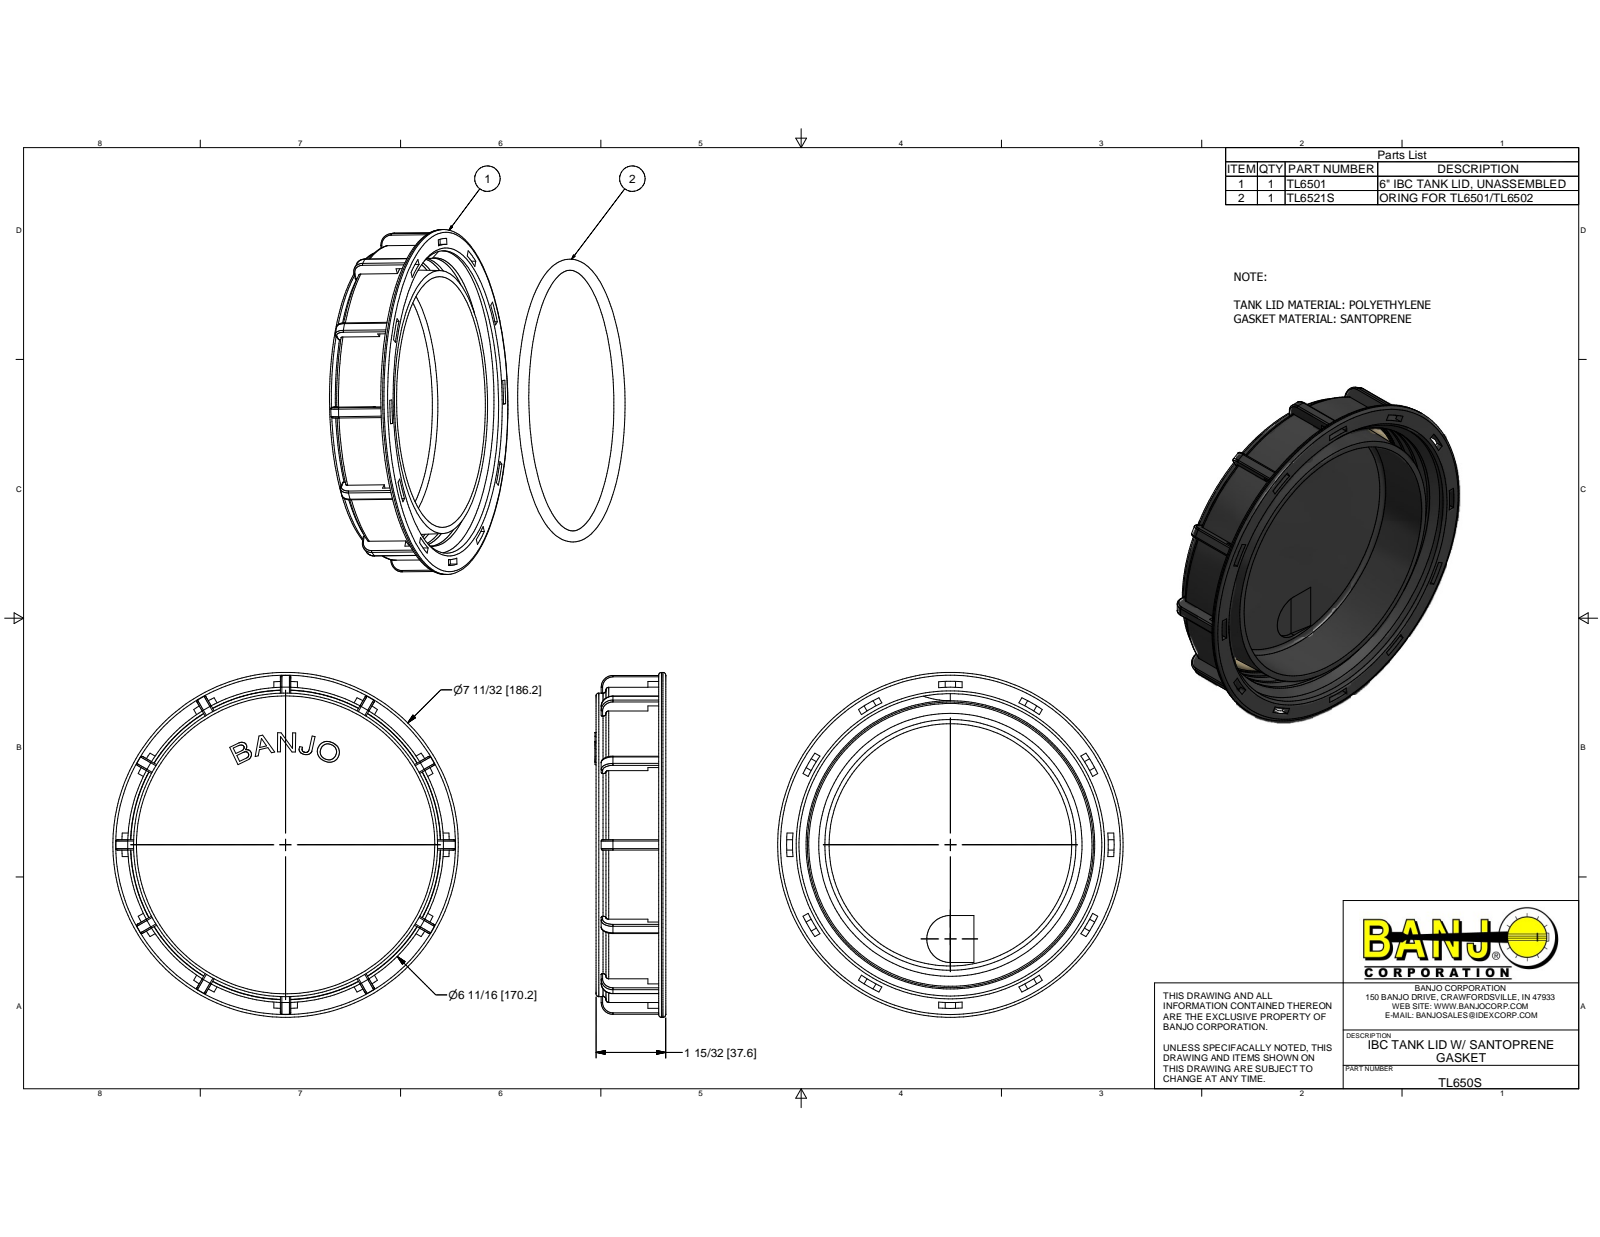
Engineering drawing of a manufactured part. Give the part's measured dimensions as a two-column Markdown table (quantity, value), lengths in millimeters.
| quantity | value |
| --- | --- |
| part name | TL650S; TL6501; TL6521S |
| STEP written by | Autodesk Inventor 2022 (AUTOMOTIVE_DESIGN) |
| units | millimeters |
| bodies | 2 solids, 329 faces (153 planar, 87 cylindrical, 89 other) |
| overall size | 186.2 × 186.2 × 38.1 |
| volume | 267 600 mm³ |
| surface area | 134 900 mm² |
| round holes (diameter × count) | 135.3 × 1, 154.2 × 1, 155.6 × 1, 163.2 × 1 |
| round bosses / shafts (diameter × count) | 186.2 × 1, 170.2 × 1, 163.8 × 1 |
| partial cylindrical surfaces (radius × count) | 0.8 × 44, 6.4 × 12, 12.7 × 1, 44.6 × 1, 88.3 × 1 |
| main face-to-face distances | 4.1, 37.6, 33.5, 33.8, 29.7, 3.8, 33.7, 29.7, 3.9, 8.6 |
